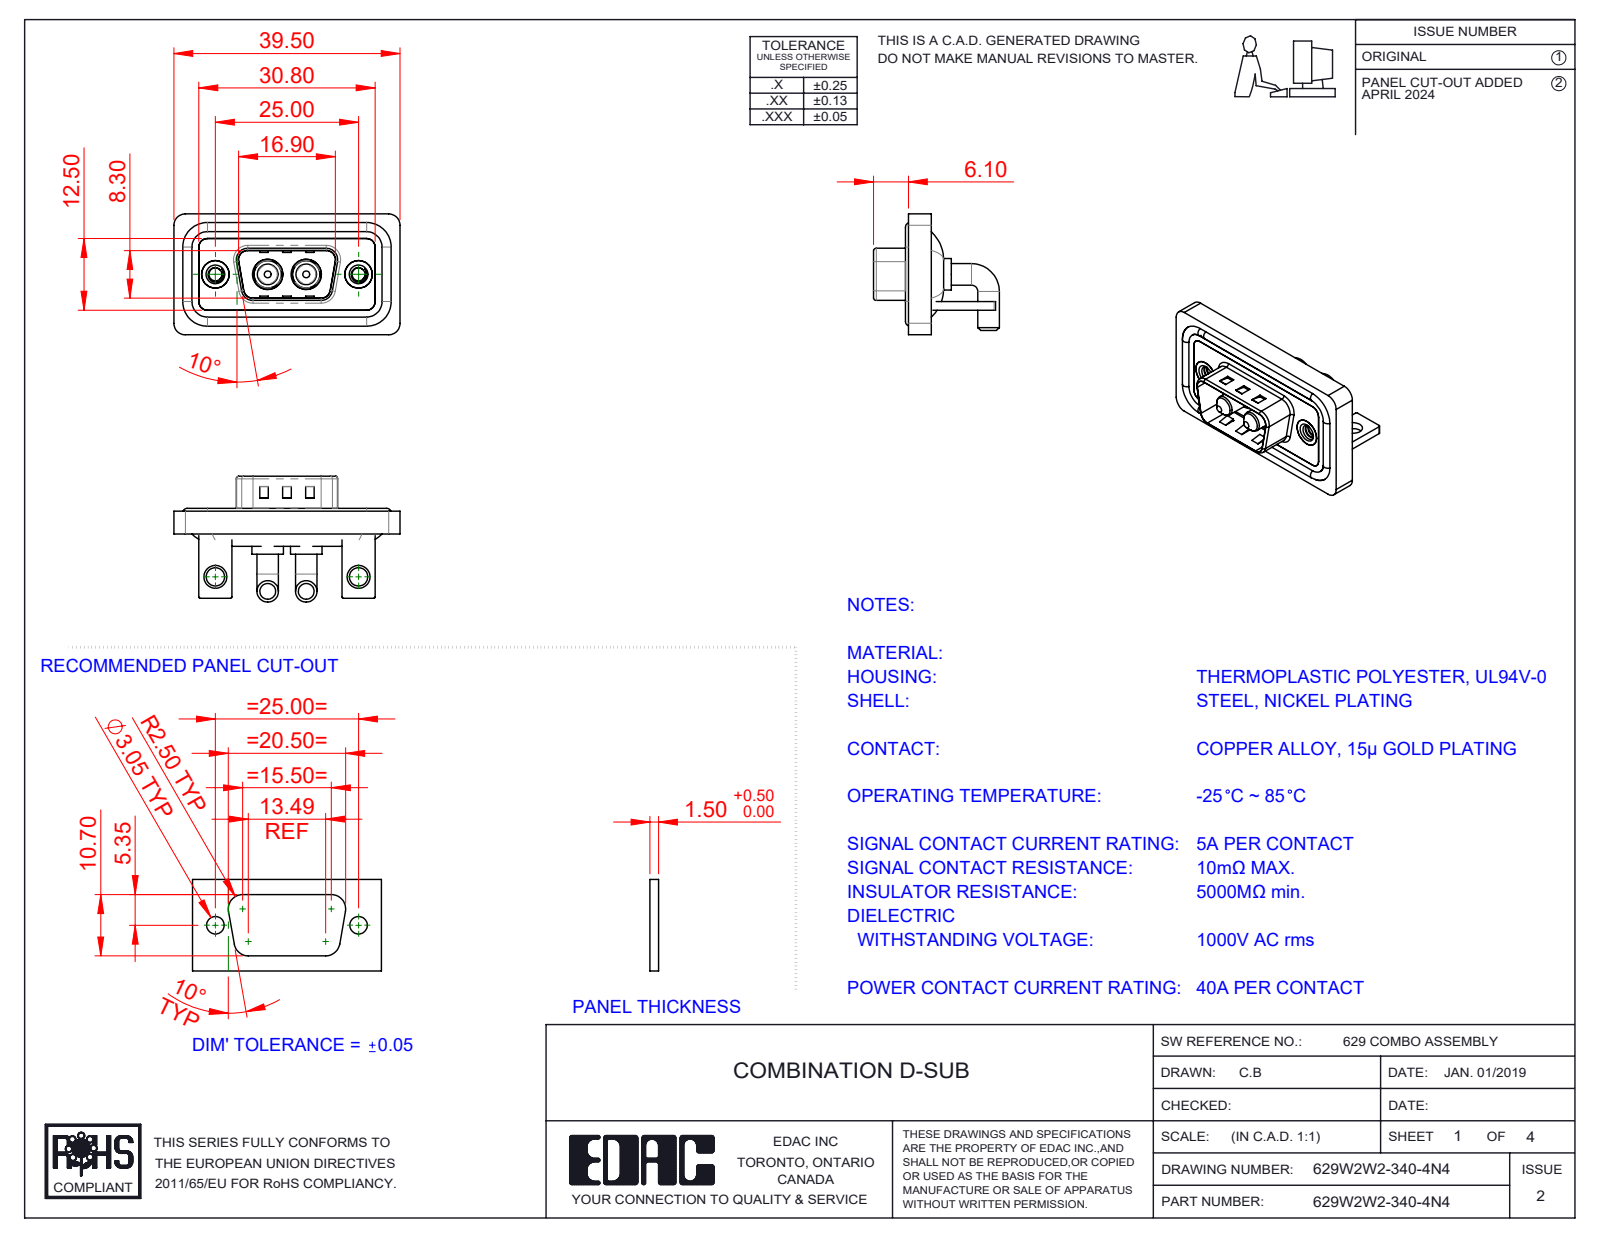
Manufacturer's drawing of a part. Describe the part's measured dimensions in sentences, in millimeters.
The part is named "629Combo Shell Rear_09 Contacts; 629Combo Waterproof Housing_09 Contacts; 629Combo Threaded Rivet_3; 629Combo Stabilizer Bracket (+4 more)". Its 3-D file was written by "SolidWorks 2023 (CONFIG_CONTROL_DESIGN)". It is 13 solids with 537 faces: 185 planar, 240 cylindrical and 112 other. Overall it measures 39.5 by 21.98 by 21.1 millimeters. Its volume is 5 008 cubic millimeters and its surface area 7 842 square millimeters. Round holes: 2 of diameter 2.26, 2 of diameter 3.2, 2 of diameter 4, 2 of diameter 4.8, 2 of diameter 4.85, 2 of diameter 5, 2 of diameter 5.3. Round bosses or shafts: 4 of diameter 3.75, 4 of diameter 1.6, 2 of diameter 5.5, 2 of diameter 5.2, 2 of diameter 4.9, 2 of diameter 4.75, 2 of diameter 3.6. Partial cylindrical surfaces (rounded edges, fillets, slot ends): 19 of radius 2, 18 of radius 1.5, 16 of radius 0.25, 9 of radius 0.5, 8 of radius 1.6, 4 of radius 0.6, 4 of radius 0.65, 4 of radius 0.9. The main face-to-face distances are 0.4, 1.5, 2.9, 0.8, 1.1, 1.2, 2.1, 1.6, 3.7, 2.5. The hole center spacings are 9.14, 15.86, 25, 6.72.
